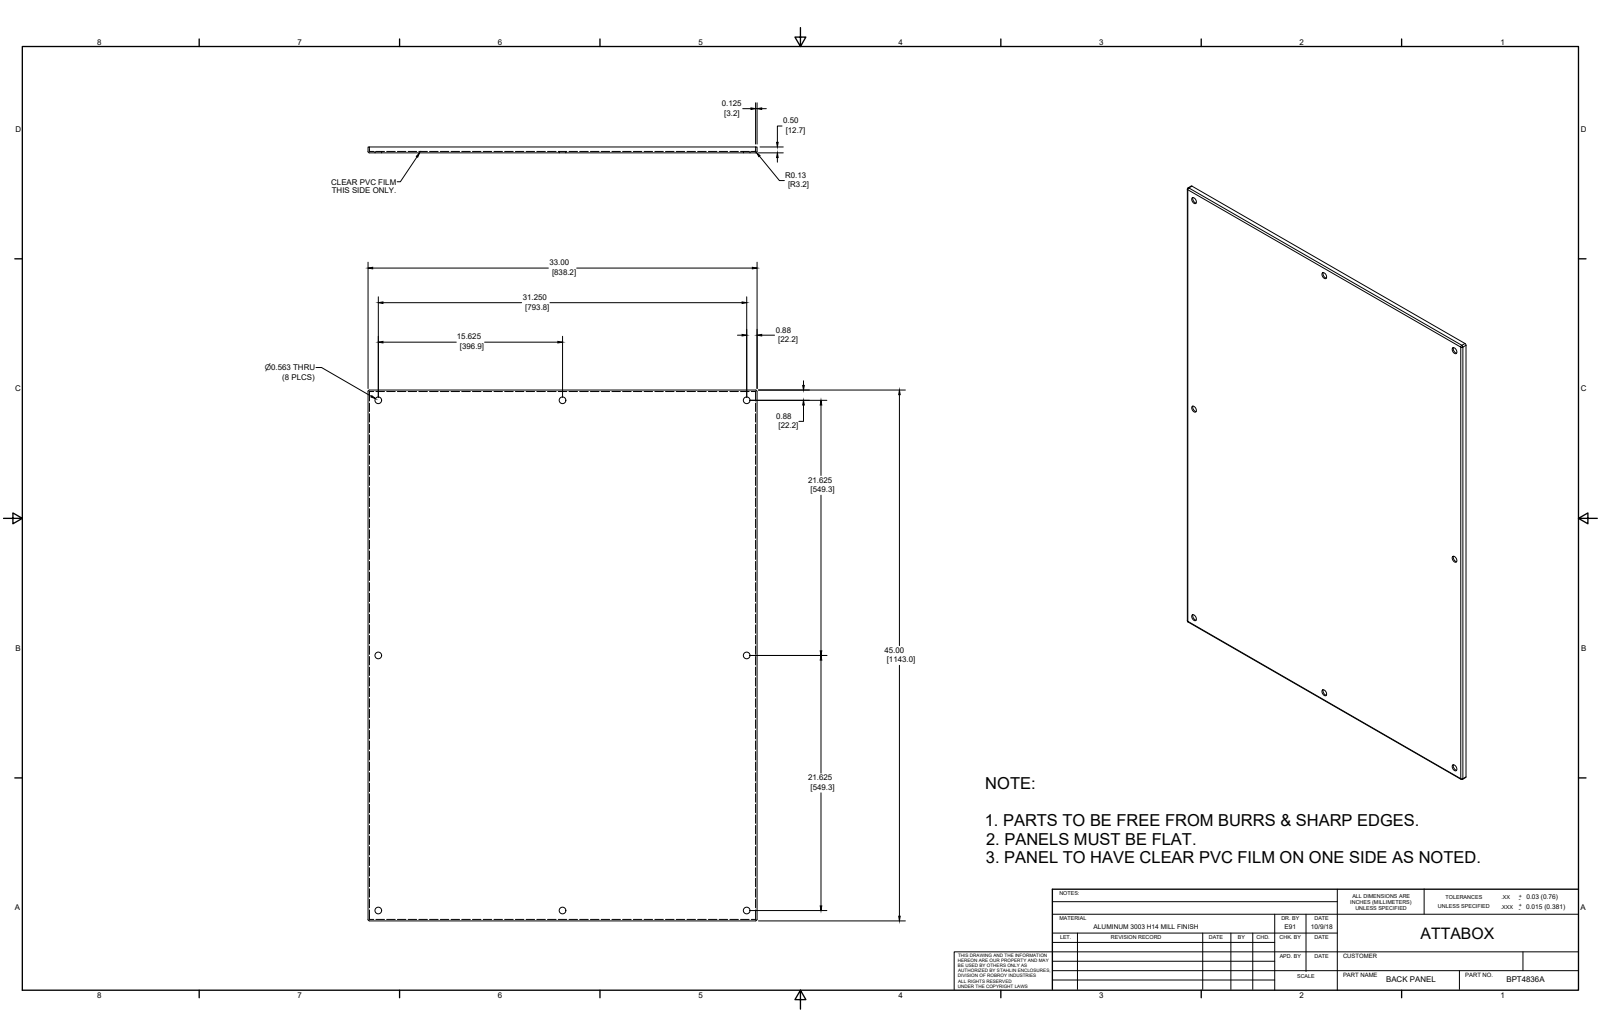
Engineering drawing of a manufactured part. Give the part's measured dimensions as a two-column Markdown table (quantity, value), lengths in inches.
| quantity | value |
| --- | --- |
| part name | BP4836AL_STP |
| STEP written by | Autodesk Inventor 2014 (AUTOMOTIVE_DESIGN) |
| units | inches |
| bodies | 1 solid, 31 faces (11 planar, 16 cylindrical, 4 other) |
| overall size | 45 × 33 × 0.5 |
| volume | 192.2 in³ |
| surface area | 3 095 in² |
| round holes (diameter × count) | 0.563 × 8 |
| partial cylindrical surfaces (radius × count) | 0.125 × 8 |
| main face-to-face distances | 0.125, 32.875, 44.875, 0.375, 0.5, 33, 32.75, 45, 44.75 |
| hole center spacings | 15.625, 21.625, 26.679, 38.003, 45.985, 31.25, 43.25, 53.358 |
